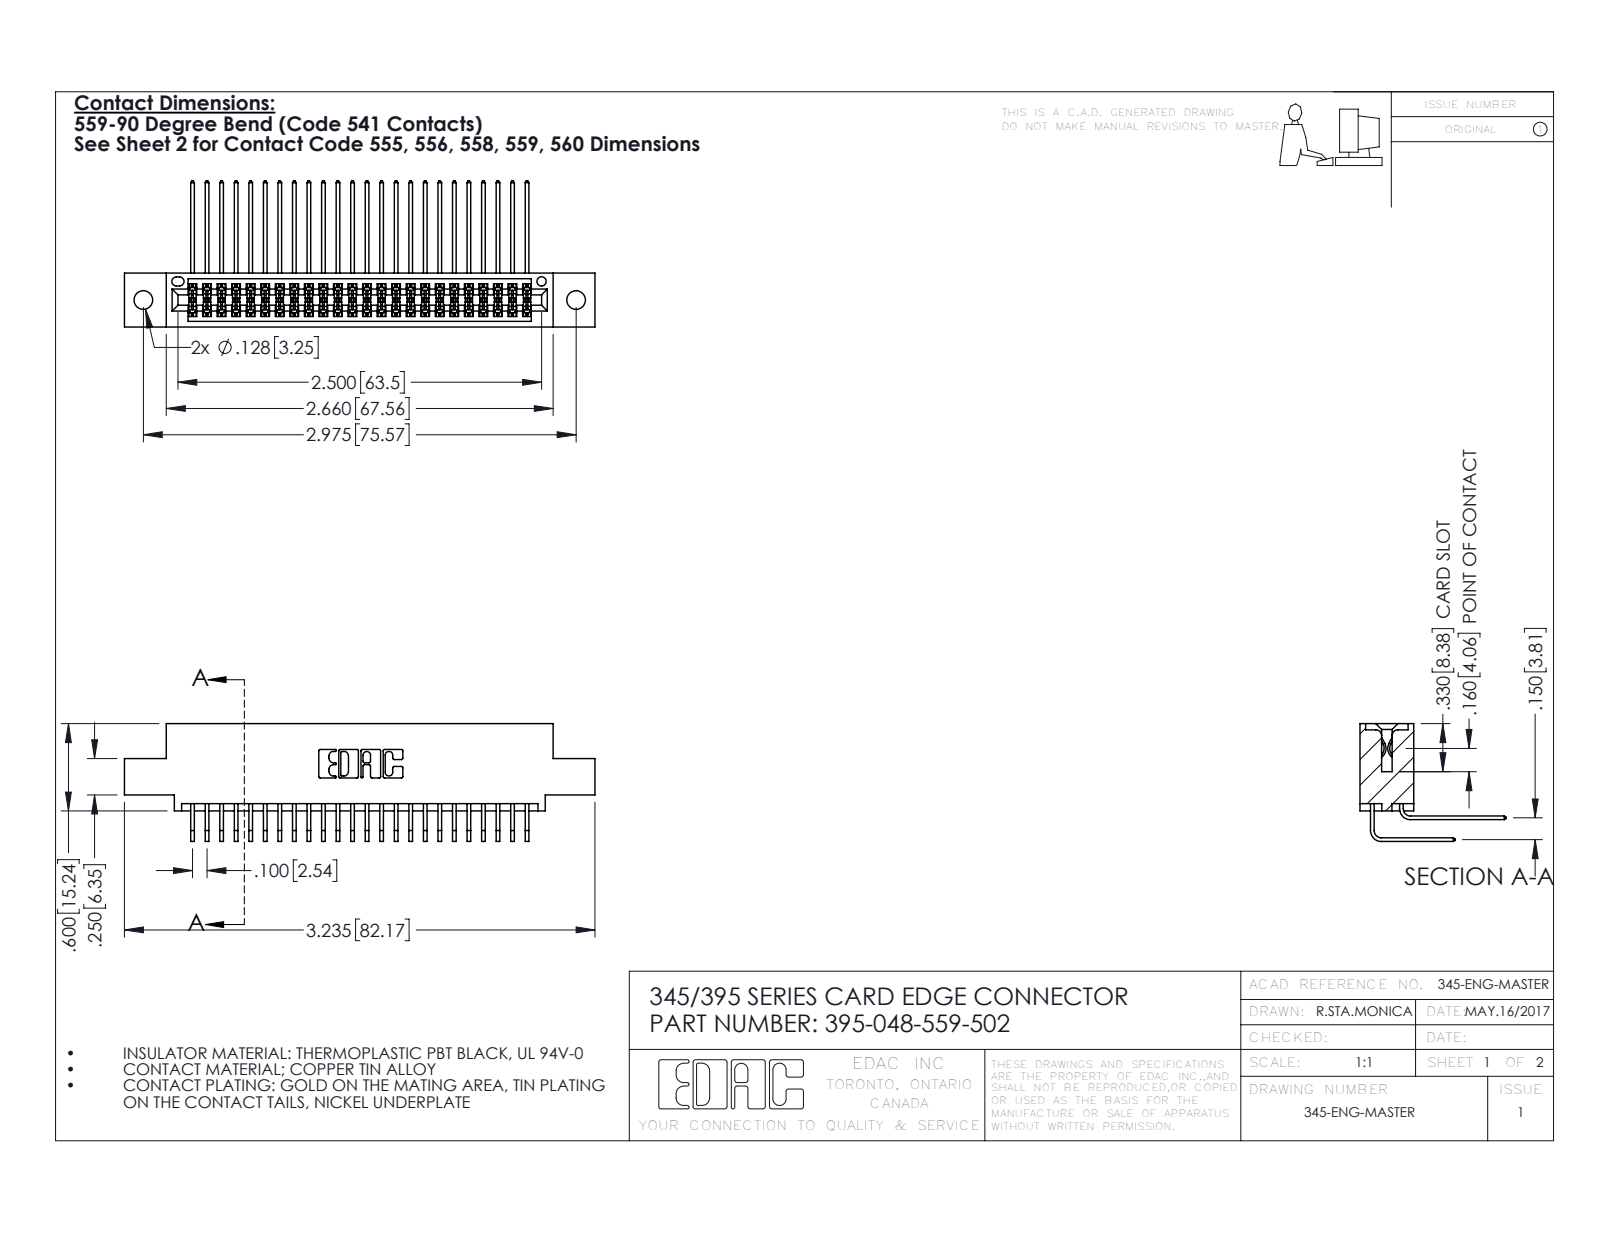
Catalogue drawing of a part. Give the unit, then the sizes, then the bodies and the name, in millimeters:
Units: millimetres
Overall size (bounding box): 82.2 × 25.5 × 20.5
Round holes (diameter × count): ⌀3.3 ×2, ⌀1.6 ×1
Partial cylindrical surfaces — rounded edges, fillets, slot ends (radius × count): R0.2 ×72, R0.3 ×22, R0.2 ×6, R0.8 ×6, R0.7 ×3, R0.4 ×2, R0.5 ×2, R0.6 ×2
Main face-to-face distances: 1.8, 7.6, 5.1, 9.4, 2.5, 6.9, 0.6, 5.7, 3.8, 4.4
Hole centre spacings: 6.9, 69.6, 75.6
Volume: 7 980 mm³ · Surface area: 12 570 mm²
Bodies: 49 solids, 2626 faces (1764 planar, 862 cylindrical, 0 other)
Part name (STEP PRODUCT): 345 Part_0.110 Offset - 0.128 Dia; 345-292-001_558 559 Tail - 1; 345-292-001_559 Tail - 2; 395-048-559-502
STEP written by: SolidWorks 2016 (CONFIG_CONTROL_DESIGN)
